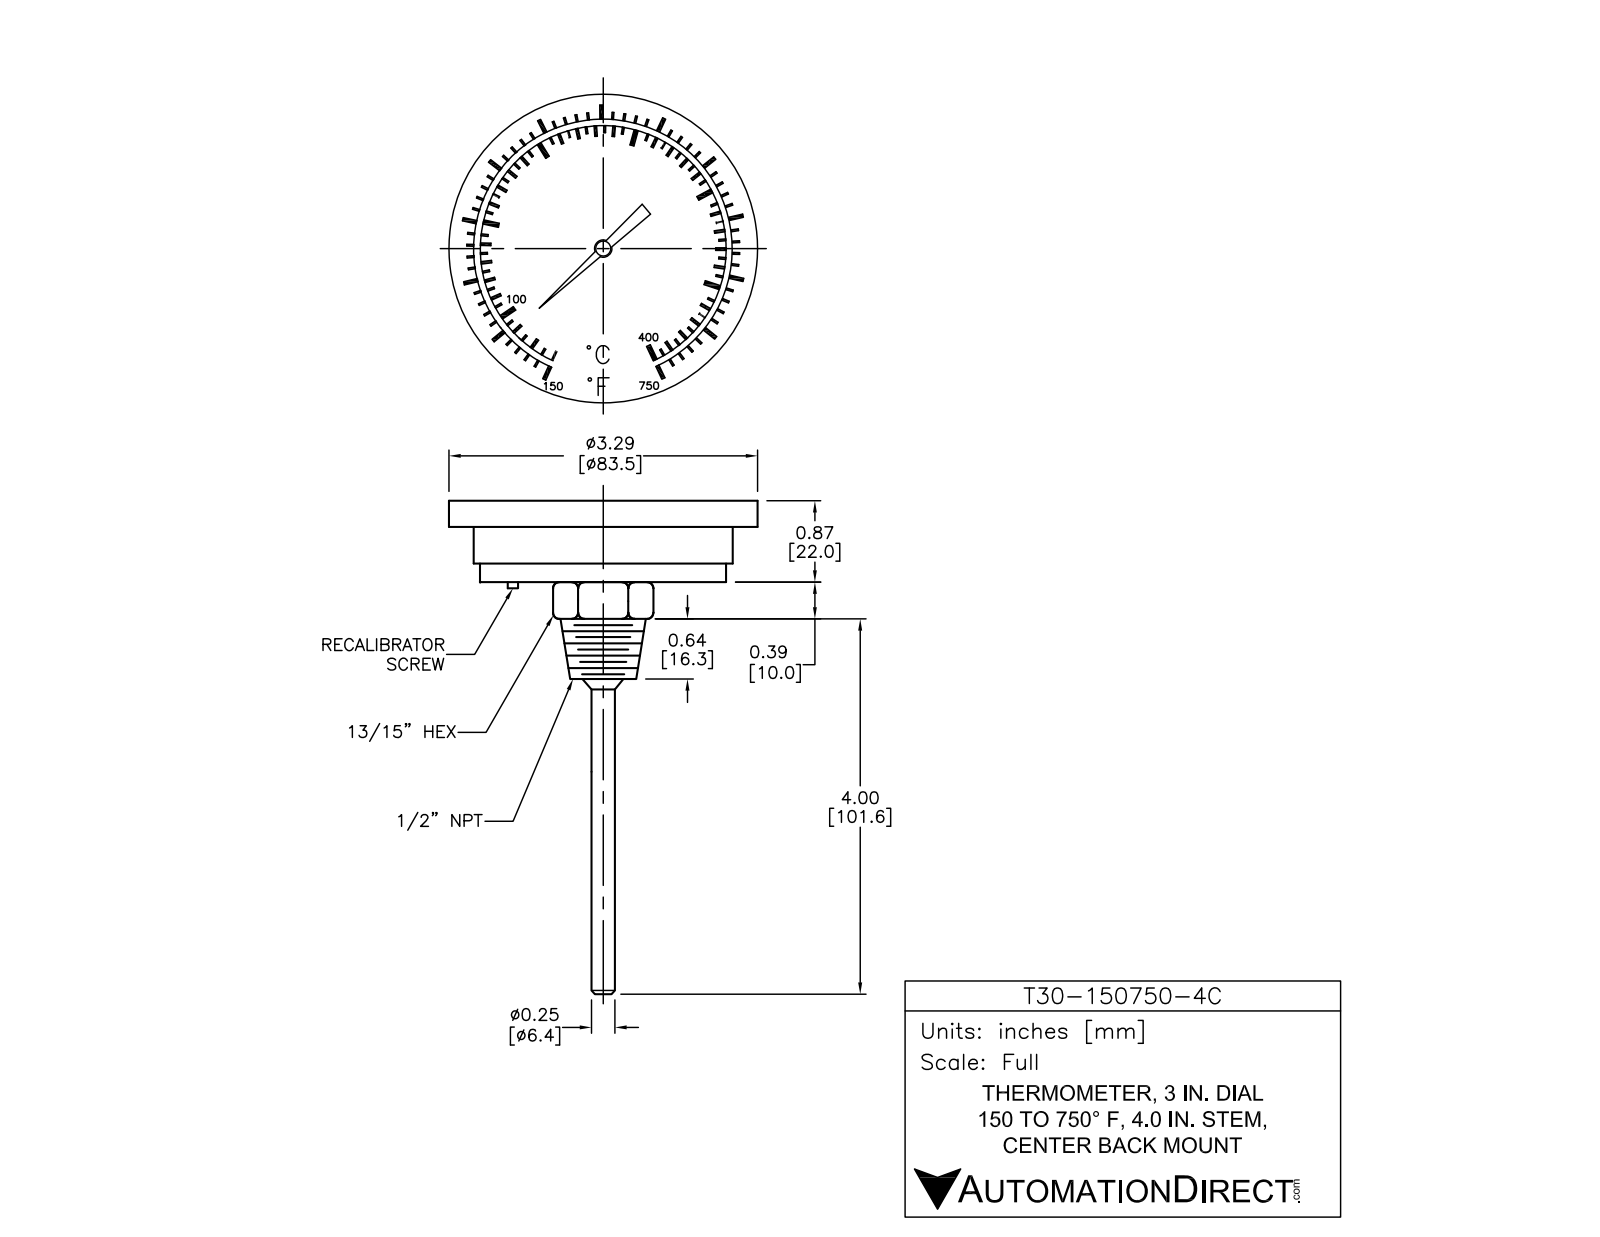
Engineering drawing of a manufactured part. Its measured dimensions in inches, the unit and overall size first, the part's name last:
Units: inches
Overall size (bounding box): 5.26 × 3.29 × 3.29
Round holes (diameter × count): ⌀0.067 ×1, ⌀2.69 ×1
Round bosses / shafts (diameter × count): ⌀3.29 ×1, ⌀2.76 ×1, ⌀2.62 ×1, ⌀0.845 ×1, ⌀0.258 ×1
Partial cylindrical surfaces — rounded edges, fillets, slot ends (radius × count): R0.04 ×1, R0.859 ×1, R0.969 ×1
Main face-to-face distances: 0.222, 0.078, 0.3, 0.87, 0.648, 0.57, 0.29, 0.59, 0.368, 0.28
Volume: 3.15 in³ · Surface area: 34.1 in²
Bodies: 58 solids, 944 faces (735 planar, 124 cylindrical, 85 other)
Part name (STEP PRODUCT): T30-150750-4C
STEP written by: SolidWorks 2021 (AUTOMOTIVE_DESIGN)
